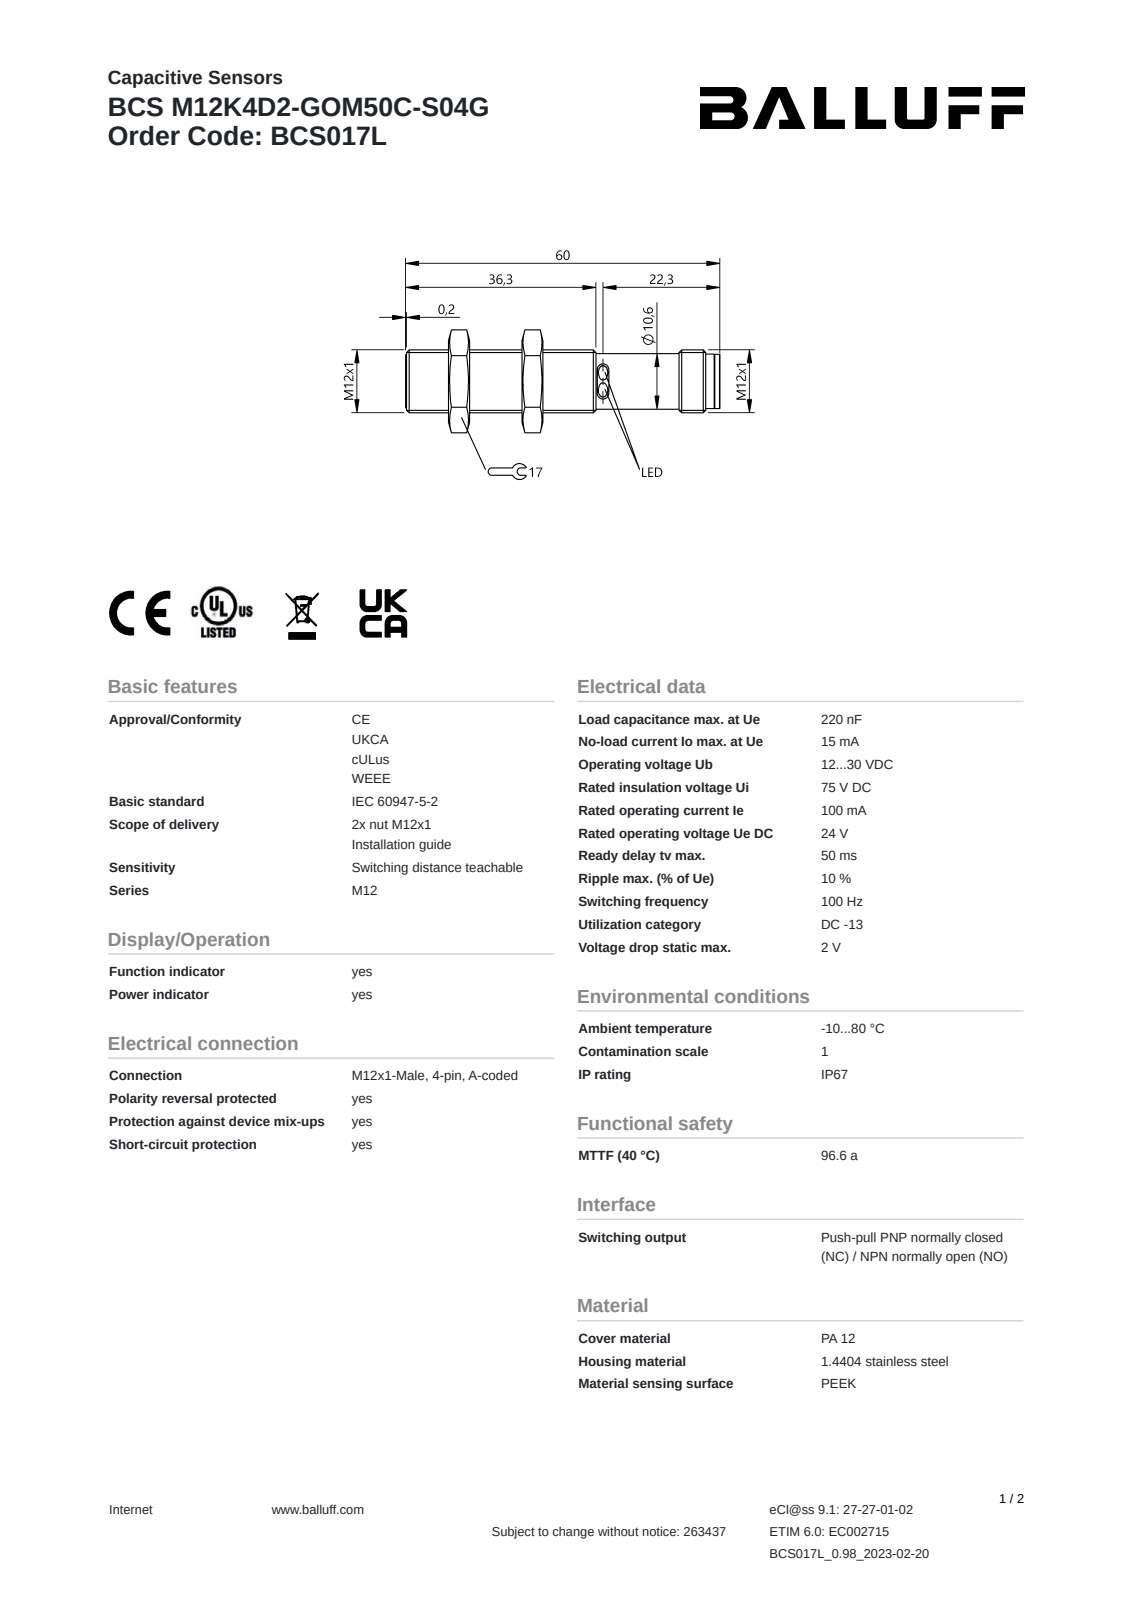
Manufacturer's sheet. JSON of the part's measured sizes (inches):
{"part_name": "BCS017L", "step_written_by": "SolidWorks 2021 (AUTOMOTIVE_DESIGN)", "units": "inches", "bodies": {"solids": 3, "faces": 111, "planar": 38, "cylindrical": 30, "other": 43}, "overall_size": [2.362, 0.773, 0.669], "volume_in3": 0.43, "surface_area_in2": 6.258, "round_holes": [[0.331, 1], [0.43, 1]], "round_bosses_or_shafts": [[0.039, 4], [0.472, 1], [0.417, 1], [0.407, 1], [0.386, 1]], "partial_cylinders_radius": [[0.028, 4], [0.075, 4], [0.012, 2], [0.043, 2], [0.024, 1], [0.18, 1], [0.182, 1]], "face_to_face_distances": [0.551, 0.157, 0.669, 0.709, 0.394, 1.031, 0.874, 0.48, 0.323, 0.984]}
